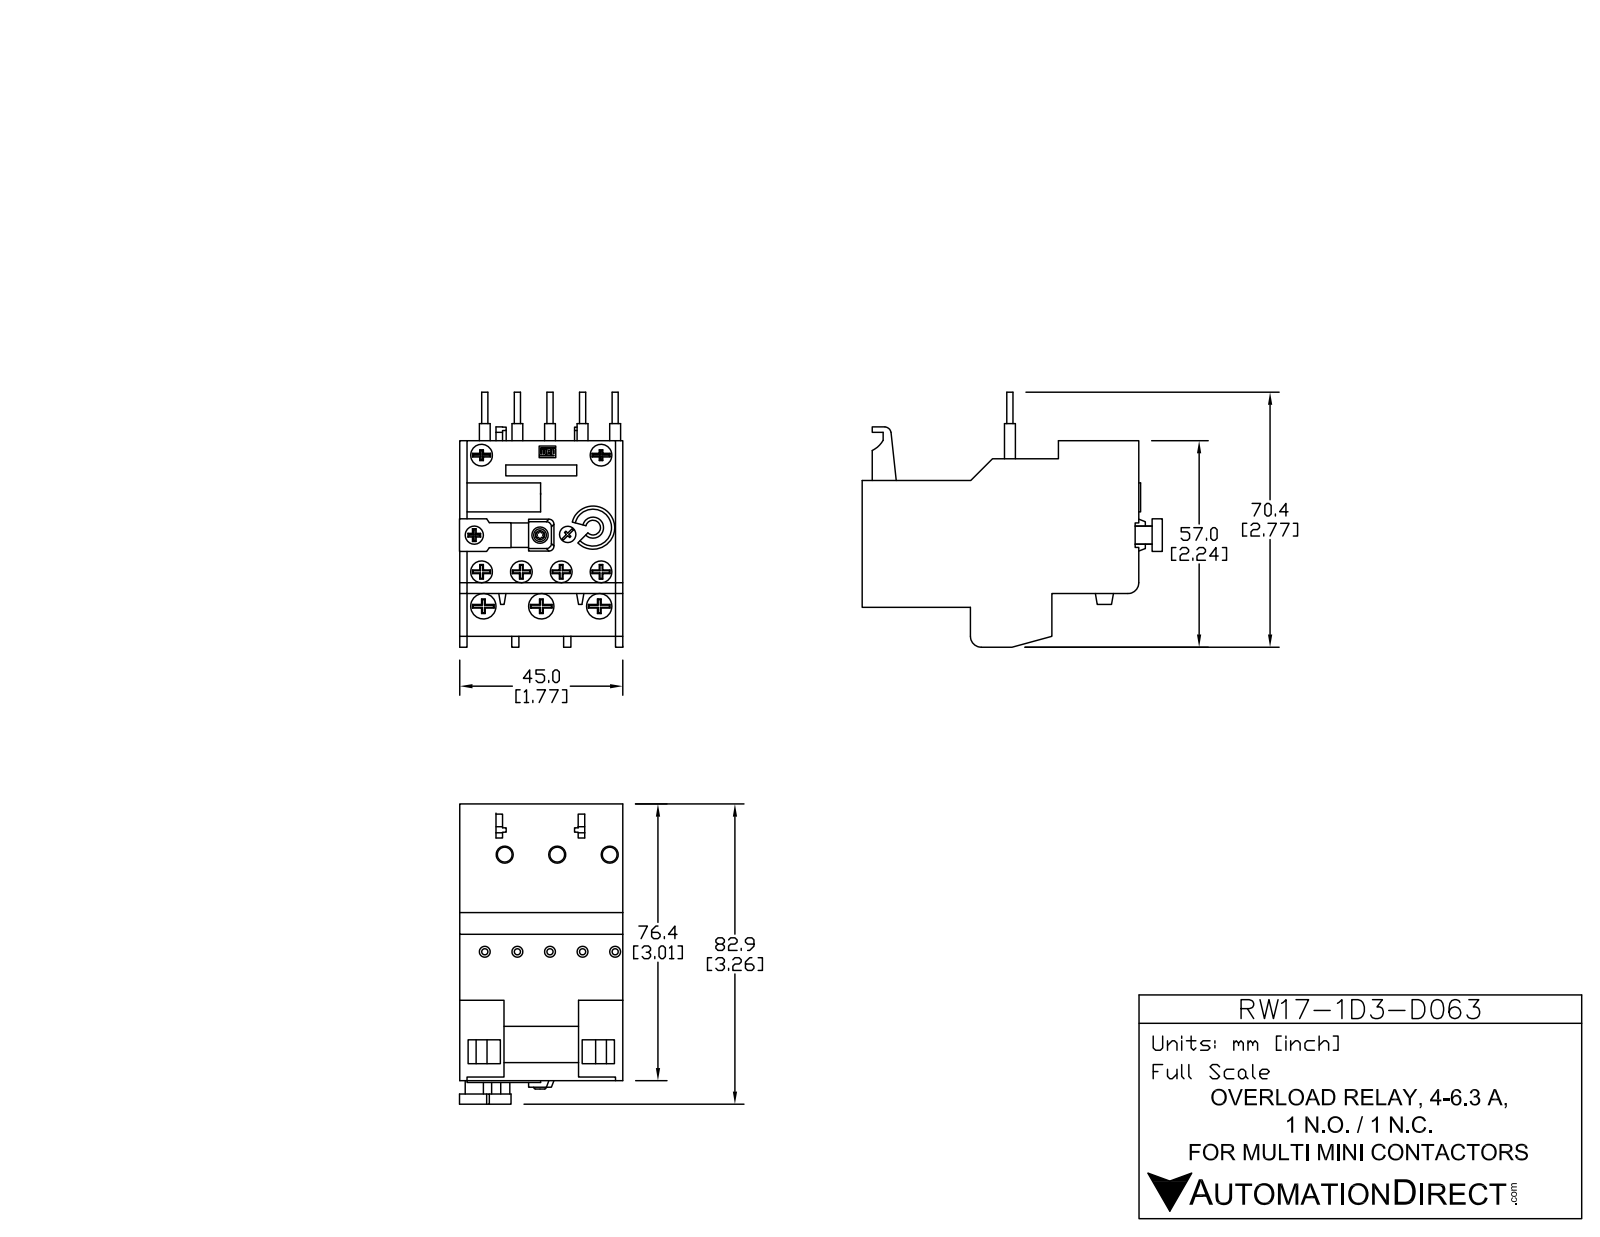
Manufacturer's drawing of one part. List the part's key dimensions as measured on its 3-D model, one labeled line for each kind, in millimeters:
Part name (STEP PRODUCT): RW17D-1D3-D063
STEP written by: SolidWorks 2013 (AUTOMOTIVE_DESIGN)
Units: millimetres
Bodies: 18 solids, 756 faces (515 planar, 214 cylindrical, 27 other)
Overall size (bounding box): 82.65 × 70.5 × 45.55
Volume: 127 454 mm³ · Surface area: 34 704 mm²
Round holes (diameter × count): ⌀6 ×6, ⌀4 ×3, ⌀7 ×3, ⌀7.5 ×3, ⌀4.5 ×1, ⌀4.75 ×1, ⌀5.33 ×1, ⌀5.5 ×1, ⌀10.42 ×1
Round bosses / shafts (diameter × count): ⌀5.5 ×7, ⌀3 ×7, ⌀1.75 ×5, ⌀5.6 ×2, ⌀3.25 ×2, ⌀6.42 ×1, ⌀6.15 ×1, ⌀4.75 ×1
Partial cylindrical surfaces — rounded edges, fillets, slot ends (radius × count): R0.5 ×20, R0.25 ×12, R1 ×9, R4.52 ×6, R5.86 ×4, R7.86 ×4, R1.5 ×3, R1.25 ×2
Main face-to-face distances: 45.5, 1.5, 10.85, 11, 76.4, 35, 1.42, 74.98, 74.9, 6
Hole centre spacings: 15, 8.55, 10.75, 30, 10.57, 11.86, 14.25, 21.35
